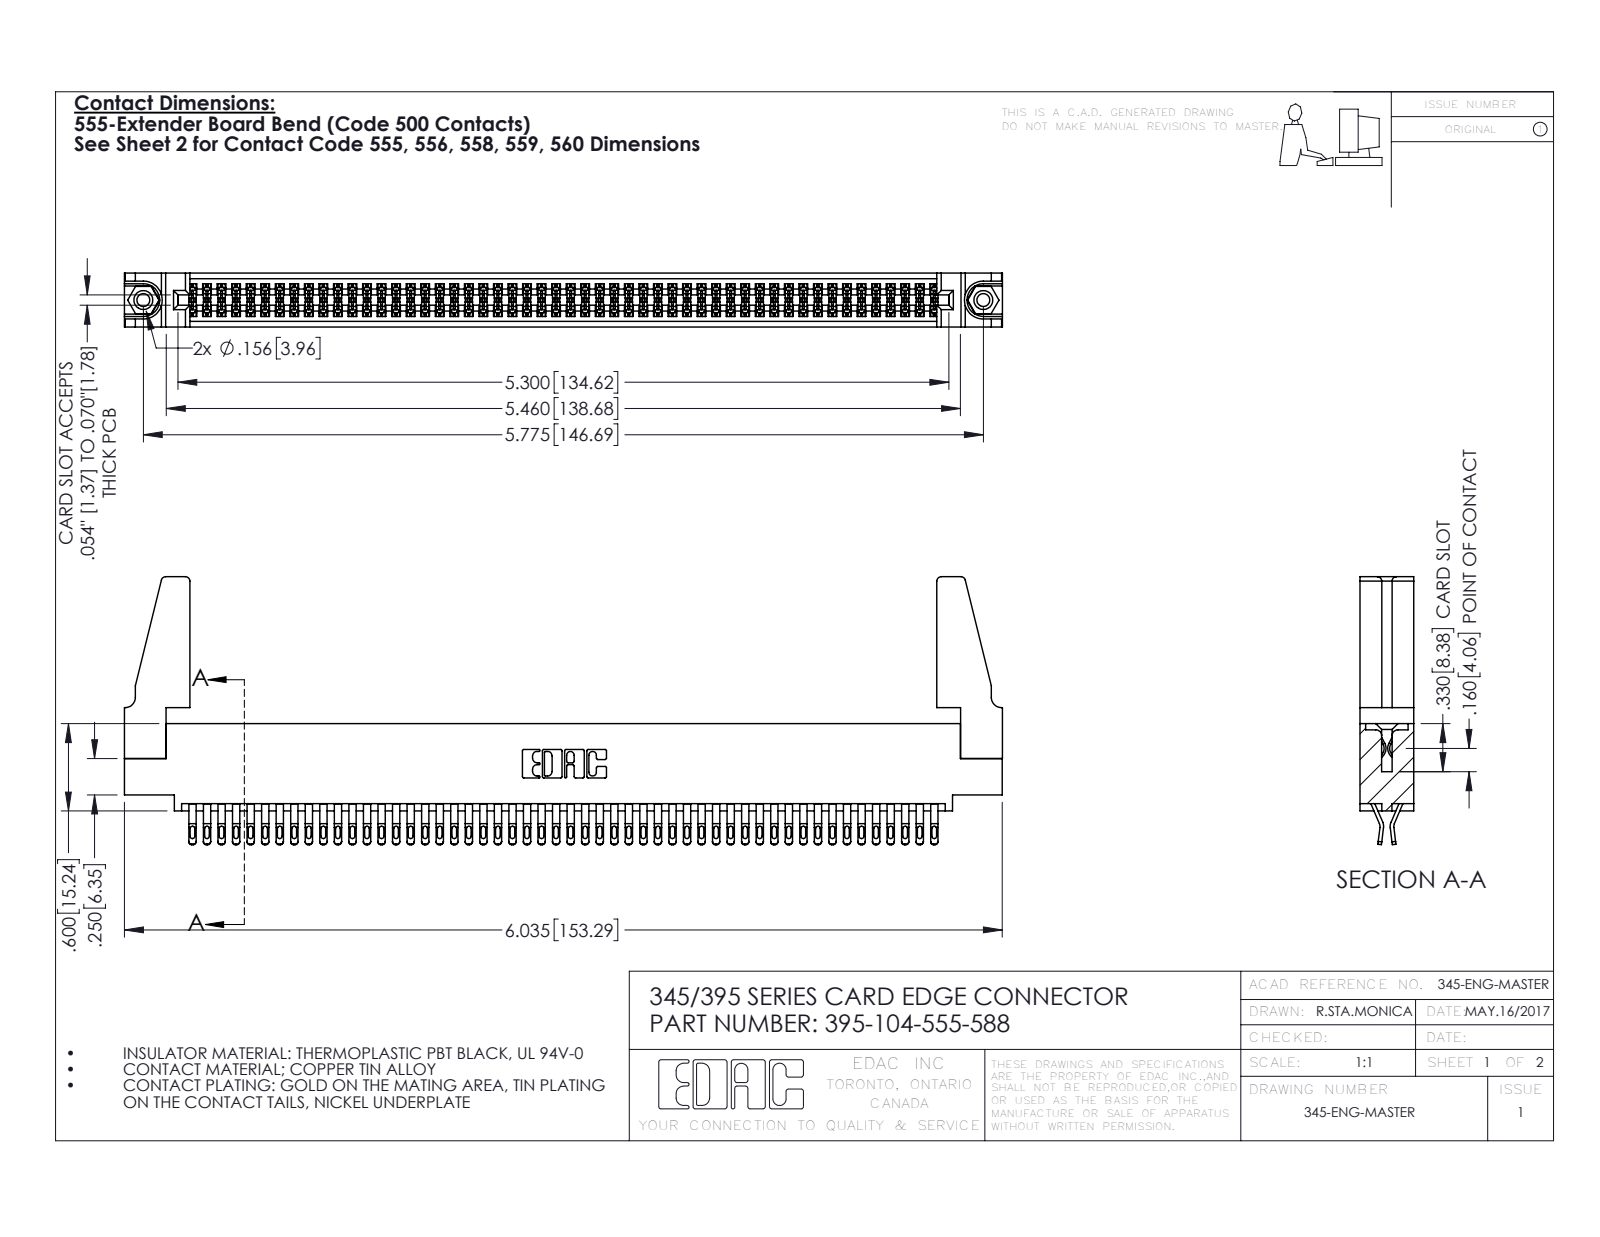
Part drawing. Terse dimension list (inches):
name: 345-292-001_555 Tail; 345-220-078_345-220-088; 395-104-555-588; 345 Part_0.110 Offset - 0.156 Dia-TH (+1 more)
written by: SolidWorks 2016 (CONFIG_CONTROL_DESIGN)
unit: in
bodies: 109 solids, 6078 faces (3380 planar, 2682 cylindrical, 16 other)
size: 6.036 × 1.842 × 0.37
volume: 1.127 in³; area: 41.77 in²
holes: 2× ⌀0.089, 2× ⌀0.125, 2× ⌀0.156, 1× ⌀0.064
bosses: 2× ⌀0.155
rounds: 260× R0.016, 208× R0.02, 156× R0.006, 22× R0.01, 8× R0.03, 6× R0.007, 6× R0.031, 3× R0.026
face distances: 0.072, 0.298, 0.37, 0.025, 0.2, 0.098, 0.272, 0.225, 0.175, 0.149
hole spacings: 0.27, 5.539, 5.775
